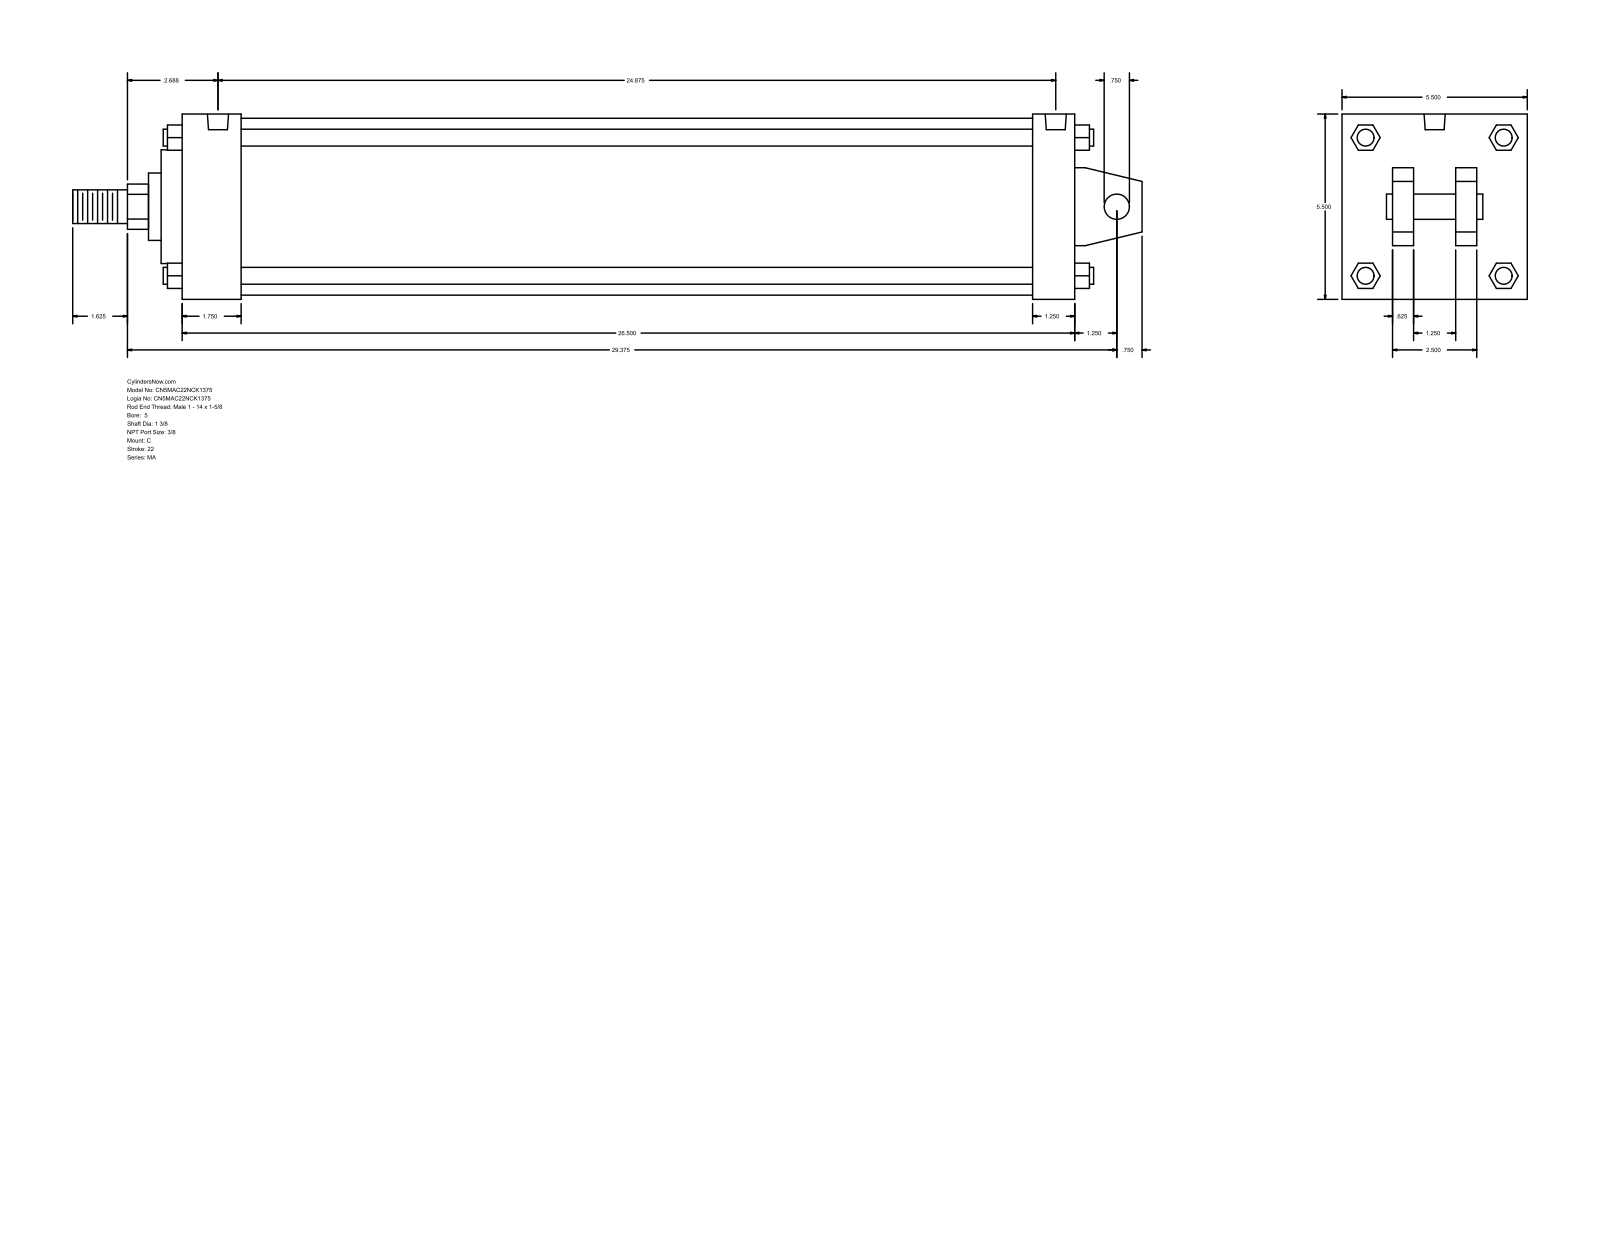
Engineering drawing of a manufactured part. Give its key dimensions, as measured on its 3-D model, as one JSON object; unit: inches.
{"part_name": "MA_C__0500_1.375", "step_written_by": "GSSL Pune (CONFIG_CONTROL_DESIGN)", "units": "inches", "bodies": {"solids": 0, "faces": 141, "planar": 109, "cylindrical": 32, "other": 0}, "overall_size": [31.75, 5.5, 5.5], "round_holes": [[0.437, 4], [0.627, 2]], "round_bosses_or_shafts": [[0.5, 4], [5.25, 1], [3.375, 1], [2, 1], [1.375, 1], [1, 1], [0.75, 1]], "partial_cylinders_radius": [[0.672, 1]], "face_to_face_distances": [5.5, 26.5, 0.625, 1.25, 25.25, 1.75, 23.5, 24.75, 2.125, 1.5], "hole_center_spacings": [24.5, 0.187, 0.188, 24.687, 24.688, 24.875]}
